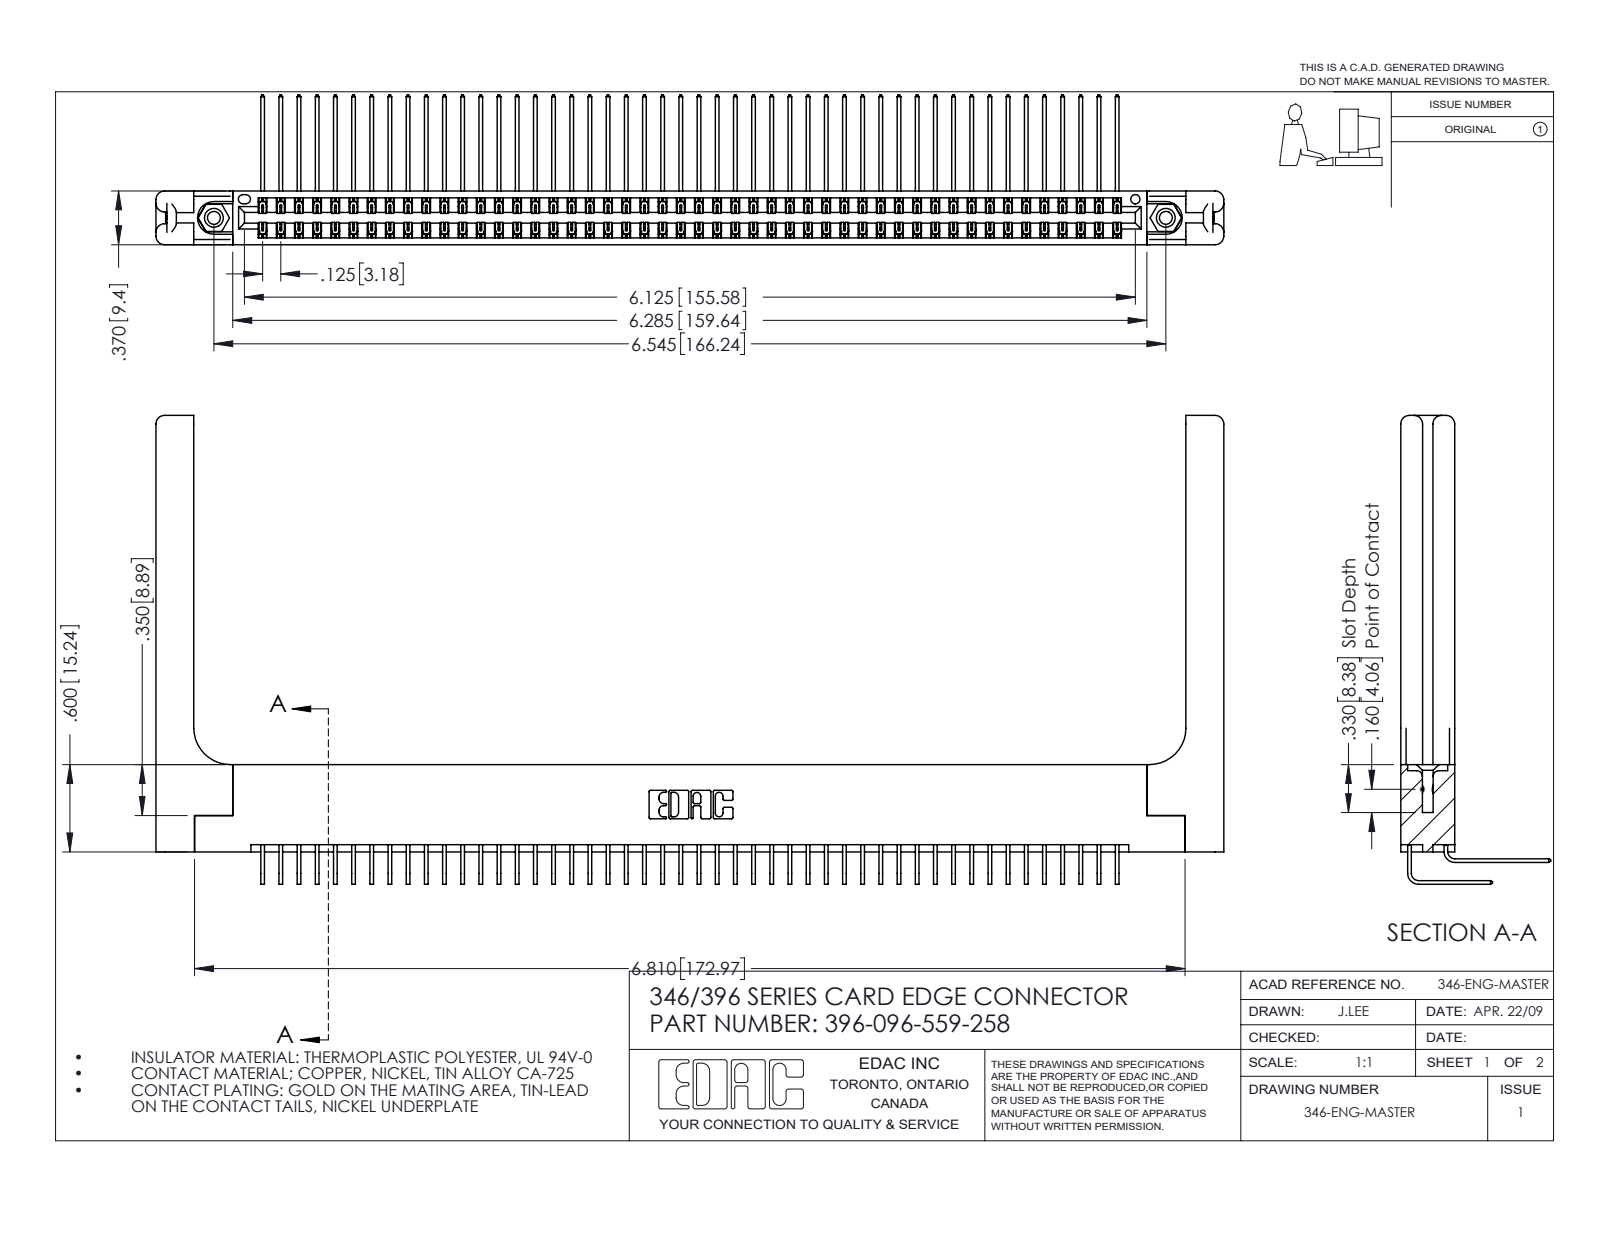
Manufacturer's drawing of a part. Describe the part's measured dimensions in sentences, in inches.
The part is named "345-292-001_558 559 Tail - 1; 396-096-559-258; 346 Part_Flush Mounting Lugs - 0.156 Dia-TH; 346-220-058_345-220-058 (+2 more)". Its 3-D file was written by "SolidWorks 2016 (CONFIG_CONTROL_DESIGN)". It is 101 solids with 5562 faces: 3776 planar, 1726 cylindrical and 60 other. Overall it measures 7.341 by 3.223 by 1.03 inches. Its volume is 1.604 cubic inches and its surface area 51.99 square inches. Round holes: 2 of diameter 0.089, 2 of diameter 0.125, 2 of diameter 0.156, 1 of diameter 0.064. Round bosses or shafts: 2 of diameter 0.155. Partial cylindrical surfaces (rounded edges, fillets, slot ends): 144 of radius 0.006, 22 of radius 0.01, 16 of radius 0.06, 6 of radius 0.007, 6 of radius 0.031, 3 of radius 0.026, 2 of radius 0.014, 2 of radius 0.022. The main face-to-face distances are 0.048, 0.322, 0.37, 0.072, 0.025, 0.25, 0.148, 0.15, 0.298, 0.275. The hole center spacings are 0.246, 6.336, 6.545.
